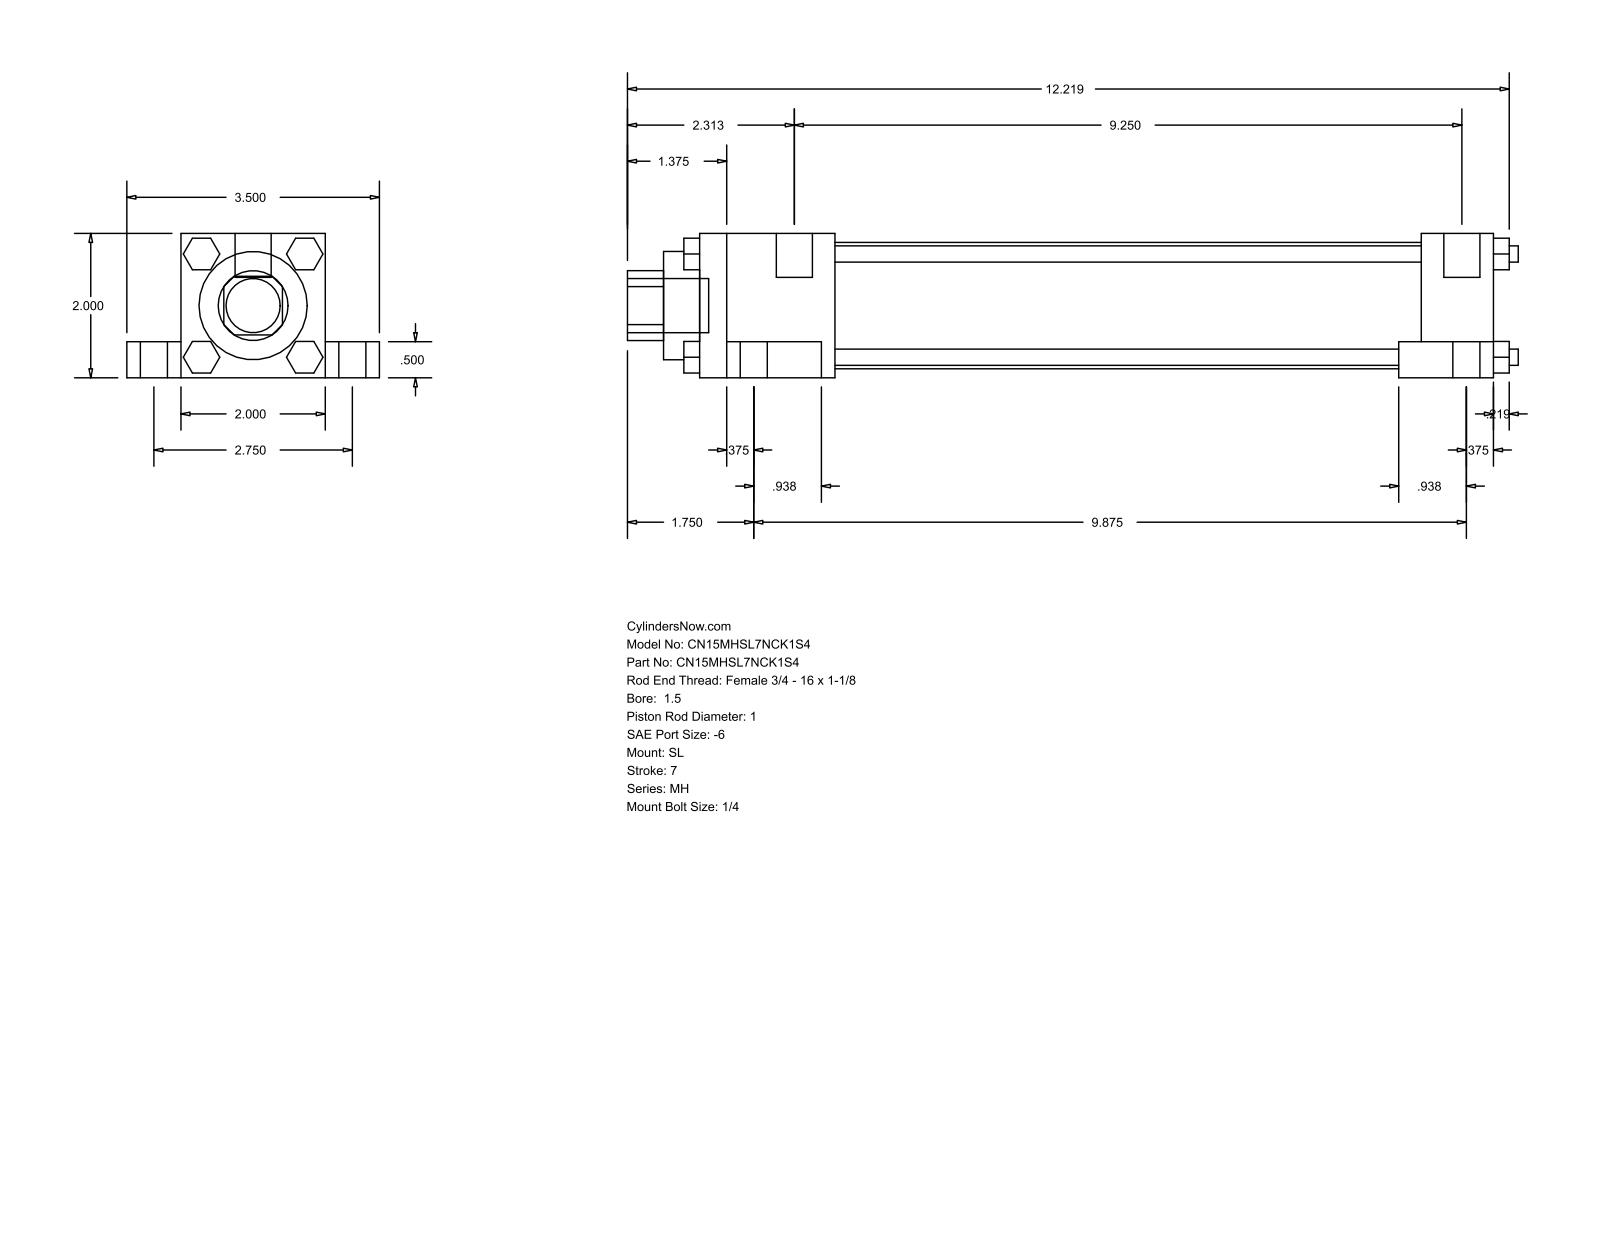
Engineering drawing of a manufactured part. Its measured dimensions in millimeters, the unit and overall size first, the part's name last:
Units: millimetres
Overall size (bounding box): 313.53 × 88.9 × 50.8
Round holes (diameter × count): ⌀25.4 ×1, ⌀38.1 ×1, ⌀44.45 ×1
Round bosses / shafts (diameter × count): ⌀15.88 ×4, ⌀9.53 ×4, ⌀5.71 ×4, ⌀5.56 ×4, ⌀12.7 ×2, ⌀19.05 ×1
Partial cylindrical surfaces — rounded edges, fillets, slot ends (radius × count): R12.29 ×1
Main face-to-face distances: 50.8, 12.7, 38.1, 19.05, 69.85, 279.4, 25.4, 9.52, 33.34, 236.54
Bodies: 0 solids, 148 faces (112 planar, 36 cylindrical, 0 other)
Part name (STEP PRODUCT): MH_SL__0150_1
STEP written by: GSSL Pune (CONFIG_CONTROL_DESIGN)
